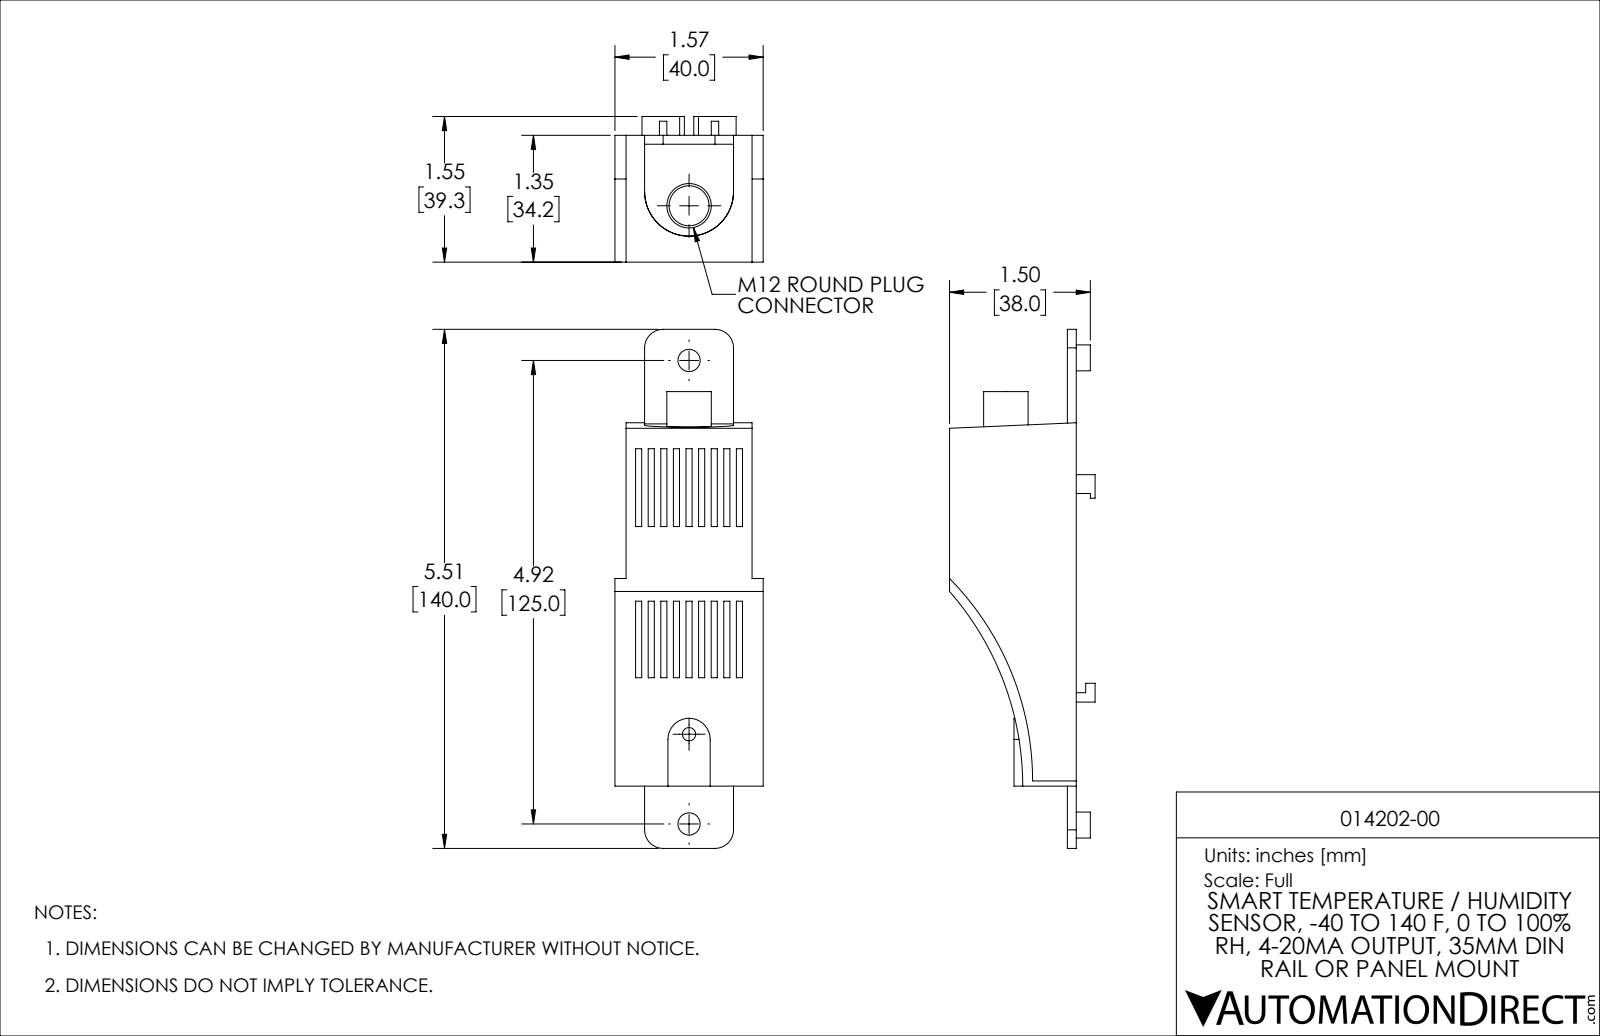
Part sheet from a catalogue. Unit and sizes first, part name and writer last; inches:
Units: inches
Overall size (bounding box): 5.512 × 1.575 × 1.546
Round holes (diameter × count): ⌀0.236 ×2, ⌀0.142 ×1, ⌀0.425 ×1
Round bosses / shafts (diameter × count): ⌀0.472 ×1
Partial cylindrical surfaces — rounded edges, fillets, slot ends (radius × count): R0.197 ×4, R0.224 ×1, R0.472 ×1, R3.059 ×1, R3.135 ×1
Main face-to-face distances: 0.134, 0.268, 0.402, 0.535, 0.065, 0.669, 0.199, 0.069, 1.339, 0.333
Hole centre spacings: 0.953, 3.969, 4.921
Volume: 5.339 in³ · Surface area: 38.61 in²
Bodies: 1 solid, 188 faces (169 planar, 19 cylindrical, 0 other)
Part name (STEP PRODUCT): PRODUCT_NAME_1
STEP written by: ACIS (AUTOMOTIVE_DESIGN_CC2)
